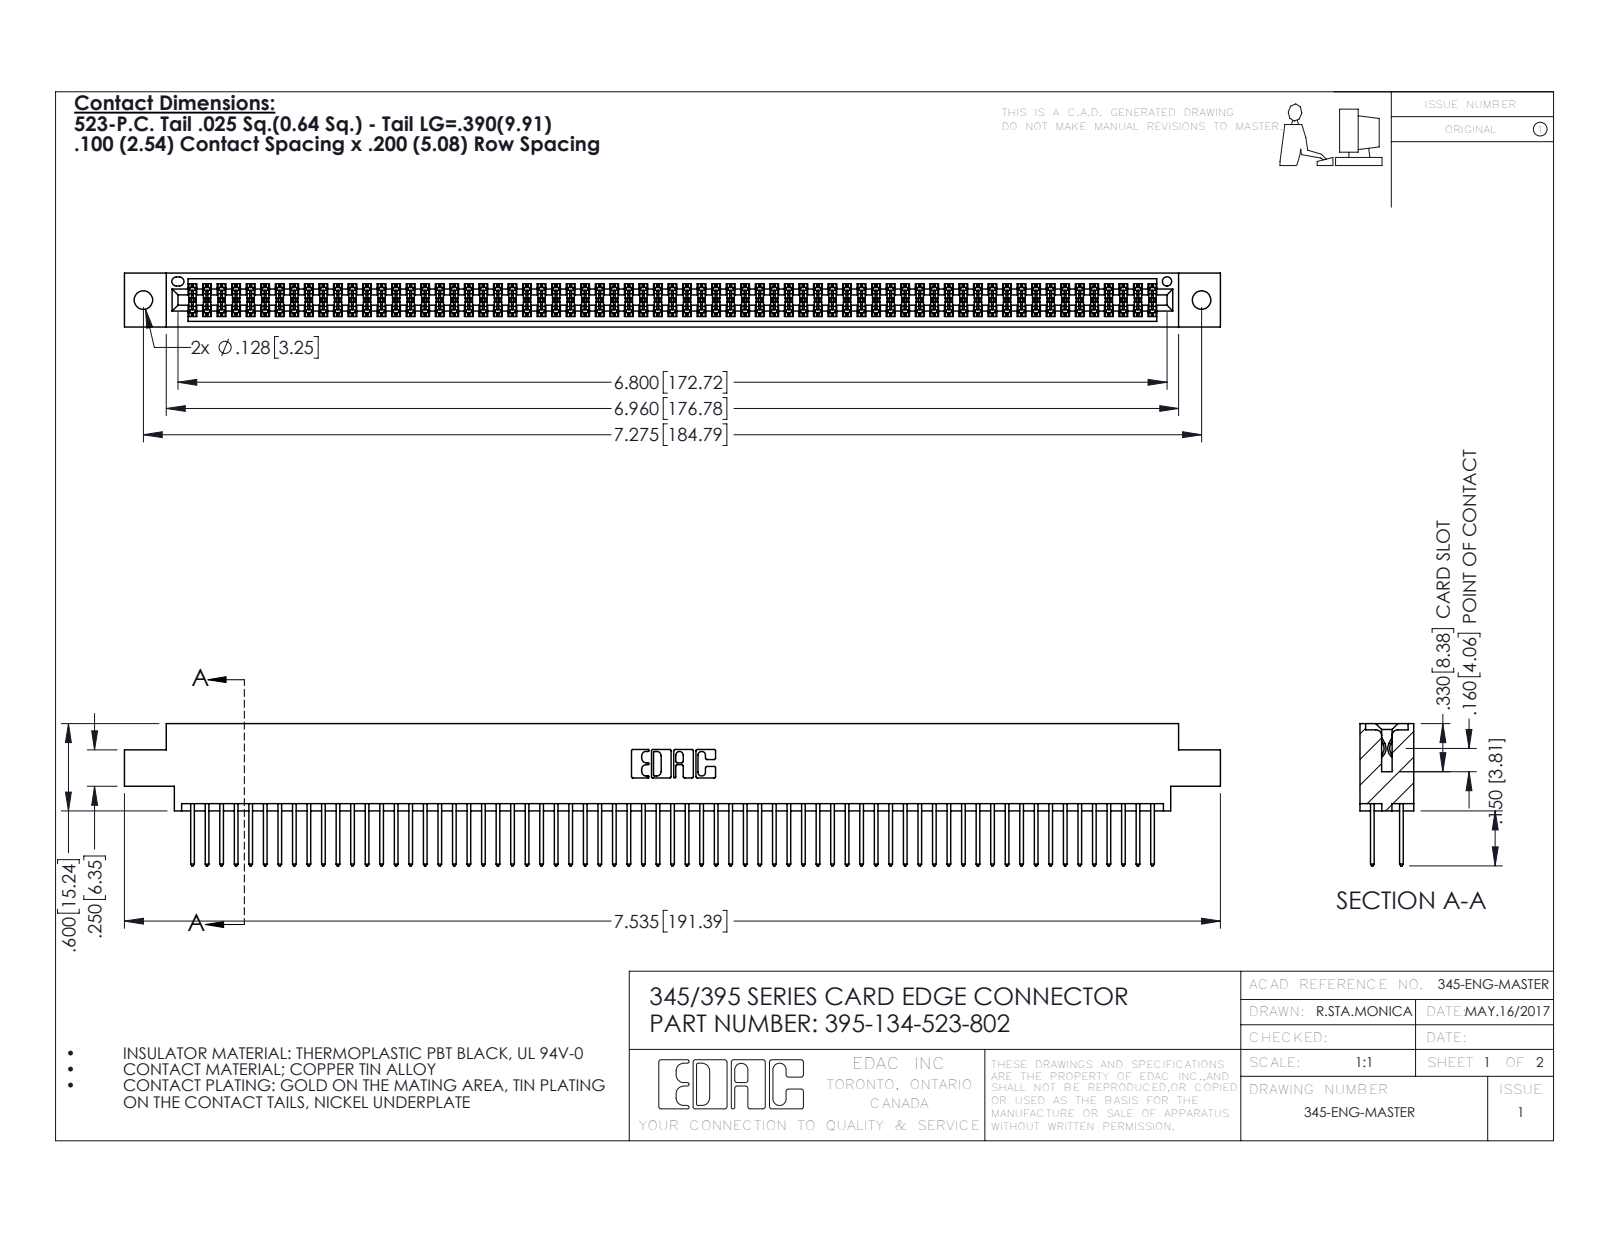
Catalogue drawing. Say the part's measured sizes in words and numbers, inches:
The part is named "345-292-001_345-293-123; 345 Part_0.170 Offset - 0.128 Dia; 395-134-523-802". Its 3-D file was written by "SolidWorks 2016 (CONFIG_CONTROL_DESIGN)". It is 135 solids with 6830 faces: 4506 planar, 2324 cylindrical and 0 other. Overall it measures 7.535 by 0.977 by 0.37 inches. Its volume is 1.156 cubic inches and its surface area 45.87 square inches. Round holes: 2 of diameter 0.128, 1 of diameter 0.064. Partial cylindrical surfaces (rounded edges, fillets, slot ends): 201 of radius 0.006, 134 of radius 0.01, 22 of radius 0.01, 6 of radius 0.007, 6 of radius 0.031, 3 of radius 0.026, 2 of radius 0.014, 2 of radius 0.019. The main face-to-face distances are 0.298, 0.072, 0.2, 0.098, 0.272, 0.025, 0.37, 0.225, 0.175, 0.149. The hole center spacings are 0.27, 7.039, 7.275.
